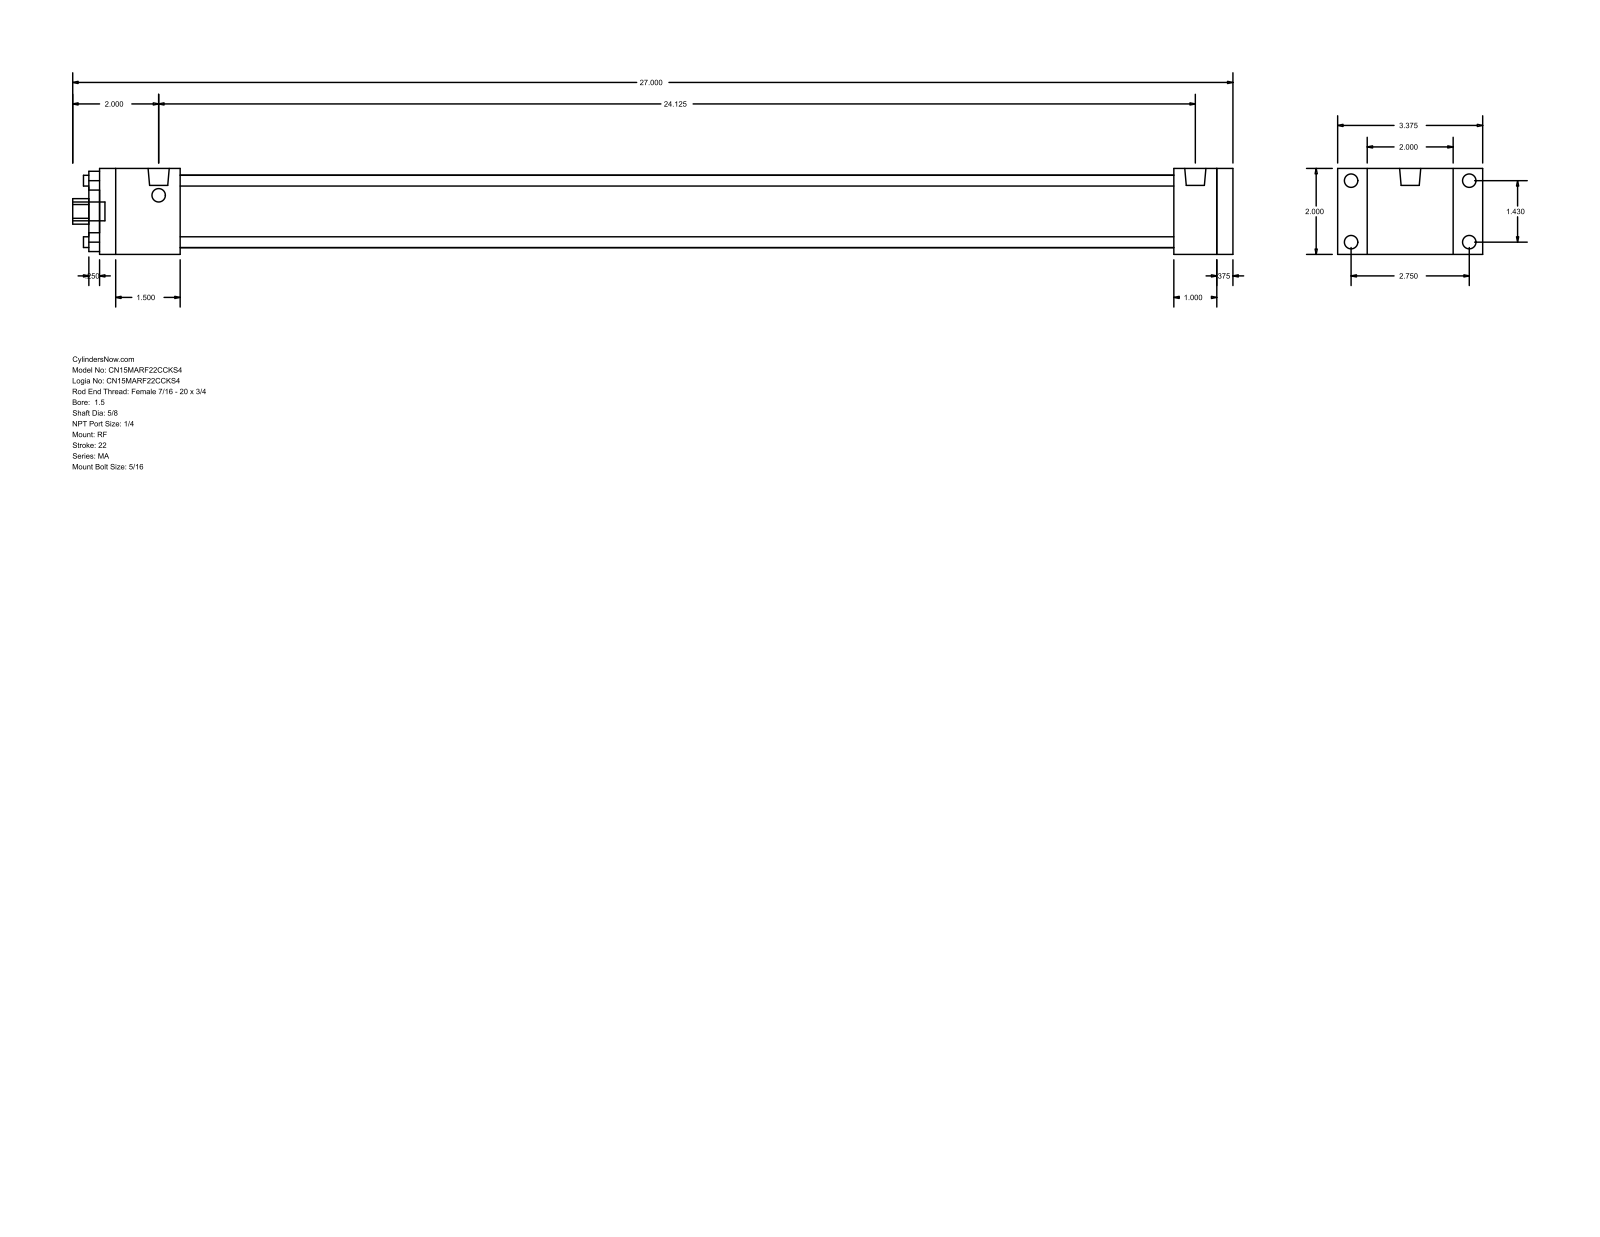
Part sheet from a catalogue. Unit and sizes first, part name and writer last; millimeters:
Units: millimetres
Overall size (bounding box): 685.8 × 85.72 × 50.8
Round holes (diameter × count): ⌀6.35 ×4, ⌀15.88 ×1, ⌀28.57 ×1, ⌀42.93 ×1
Round bosses / shafts (diameter × count): ⌀7.94 ×8, ⌀12.49 ×2, ⌀11.11 ×1
Partial cylindrical surfaces — rounded edges, fillets, slot ends (radius × count): R7.54 ×1
Main face-to-face distances: 50.8, 9.53, 669.92, 660.39, 635, 25.39, 34.92, 47.62, 587.38, 612.77
Hole centre spacings: 25.68, 36.32, 51.36
Bodies: 0 solids, 92 faces (64 planar, 28 cylindrical, 0 other)
Part name (STEP PRODUCT): MA_RF__0150_0.625
STEP written by: GSSL Pune (CONFIG_CONTROL_DESIGN)
